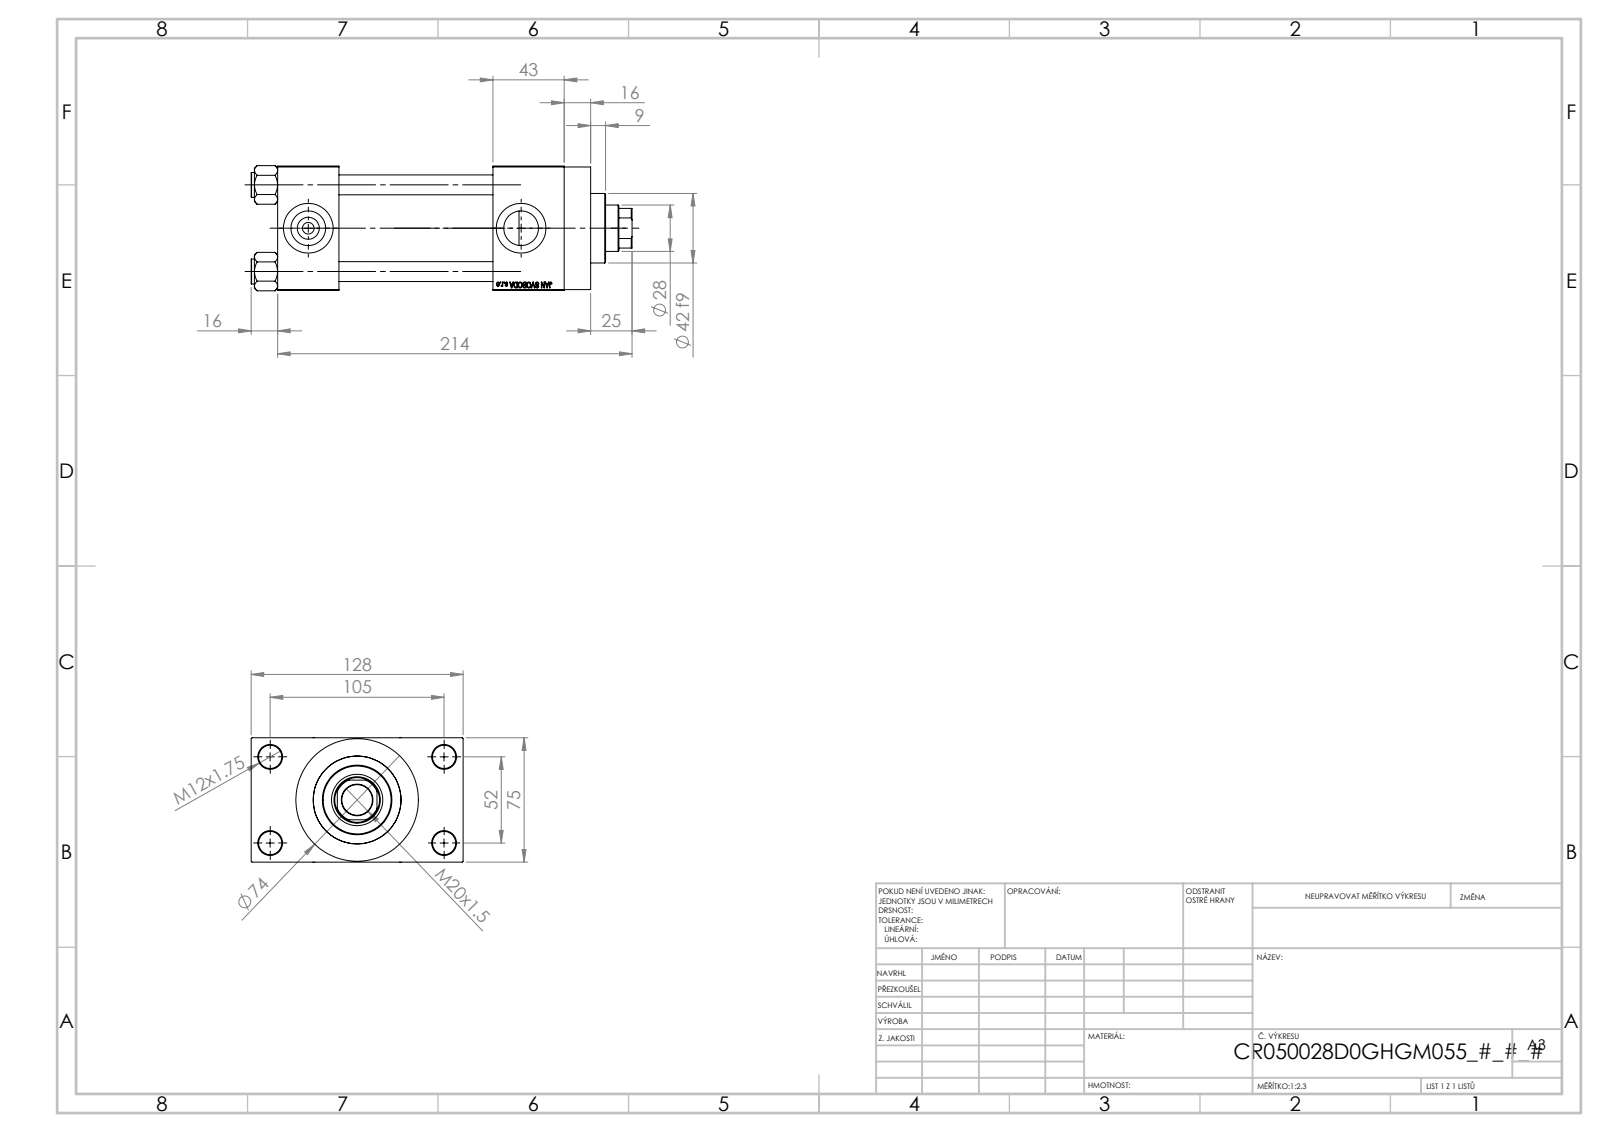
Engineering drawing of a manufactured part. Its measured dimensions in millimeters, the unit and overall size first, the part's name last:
Units: millimetres
Overall size (bounding box): 230 × 128 × 75.54
Round holes (diameter × count): ⌀12 ×4, ⌀14 ×4, ⌀7 ×2, ⌀20.96 ×2, ⌀30 ×2, ⌀18.5 ×1, ⌀28 ×1, ⌀31 ×1, ⌀41 ×1, ⌀50 ×1, ⌀53 ×1
Round bosses / shafts (diameter × count): ⌀15 ×4, ⌀74 ×1, ⌀56 ×1, ⌀42 ×1
Partial cylindrical surfaces — rounded edges, fillets, slot ends (radius × count): R13.5 ×1
Main face-to-face distances: 75, 93, 37, 130, 26.5, 173, 136, 43, 101.5, 16
Hole centre spacings: 26.35, 36.98, 52.3, 58.43, 58.59, 78.65, 94.37, 52
Volume: 861 078 mm³ · Surface area: 190 620 mm²
Bodies: 11 solids, 1103 faces (497 planar, 88 cylindrical, 518 other)
Part name (STEP PRODUCT): NUT_M5_D; V215_VC_A; V215CR_D_Body; V215CR_VCP_D (+1 more)
STEP written by: SolidWorks 2019 (CONFIG_CONTROL_DESIGN)
